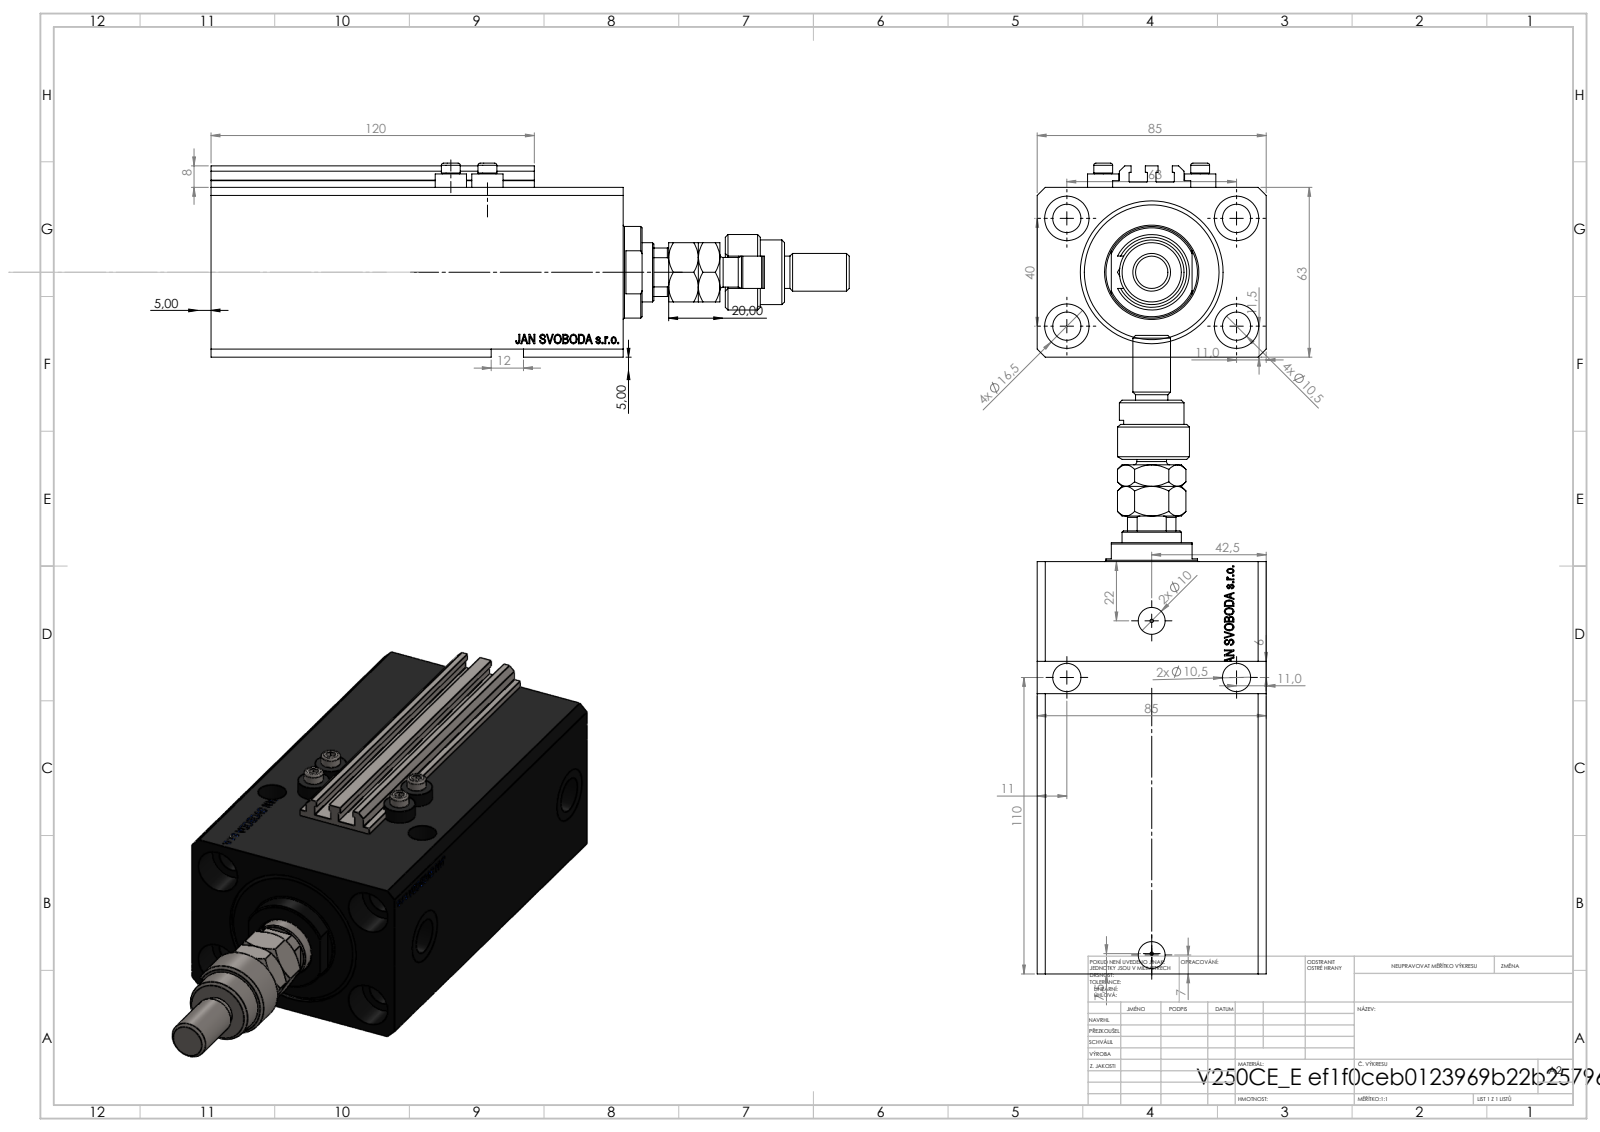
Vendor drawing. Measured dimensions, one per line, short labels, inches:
name: V250CE_E_Body; V250CE_VC_E; MFA; ALLEN BOLT V250CE (+2 more)
written by: SolidWorks 2019 (CONFIG_CONTROL_DESIGN)
unit: in
bodies: 10 solids, 1192 faces (563 planar, 159 cylindrical, 470 other)
size: 9.331 × 3.346 × 2.835
volume: 43.07 in³; area: 230.6 in²
holes: 8× ⌀0.413, 4× ⌀0.049, 4× ⌀0.157, 4× ⌀0.65, 2× ⌀0.394, 2× ⌀0.518, 2× ⌀0.787, 1× ⌀0.492, 1× ⌀0.866, 1× ⌀1.575, 1× ⌀2.087
bosses: 4× ⌀0.457, 4× ⌀0.276, 1× ⌀1.339, 1× ⌀1.102, 1× ⌀0.945, 1× ⌀0.709, 1× ⌀0.551, 1× ⌀0.472
rounds: 10× R0.008, 1× R0.384, 1× R0.413
face distances: 2.48, 3.346, 0.669, 6.024, 5.354, 0.449, 4.906, 5.575, 0.118, 2.559
hole spacings: 1.469, 2.48, 0.535, 0.606, 0.983, 1.324, 1.417, 1.491
